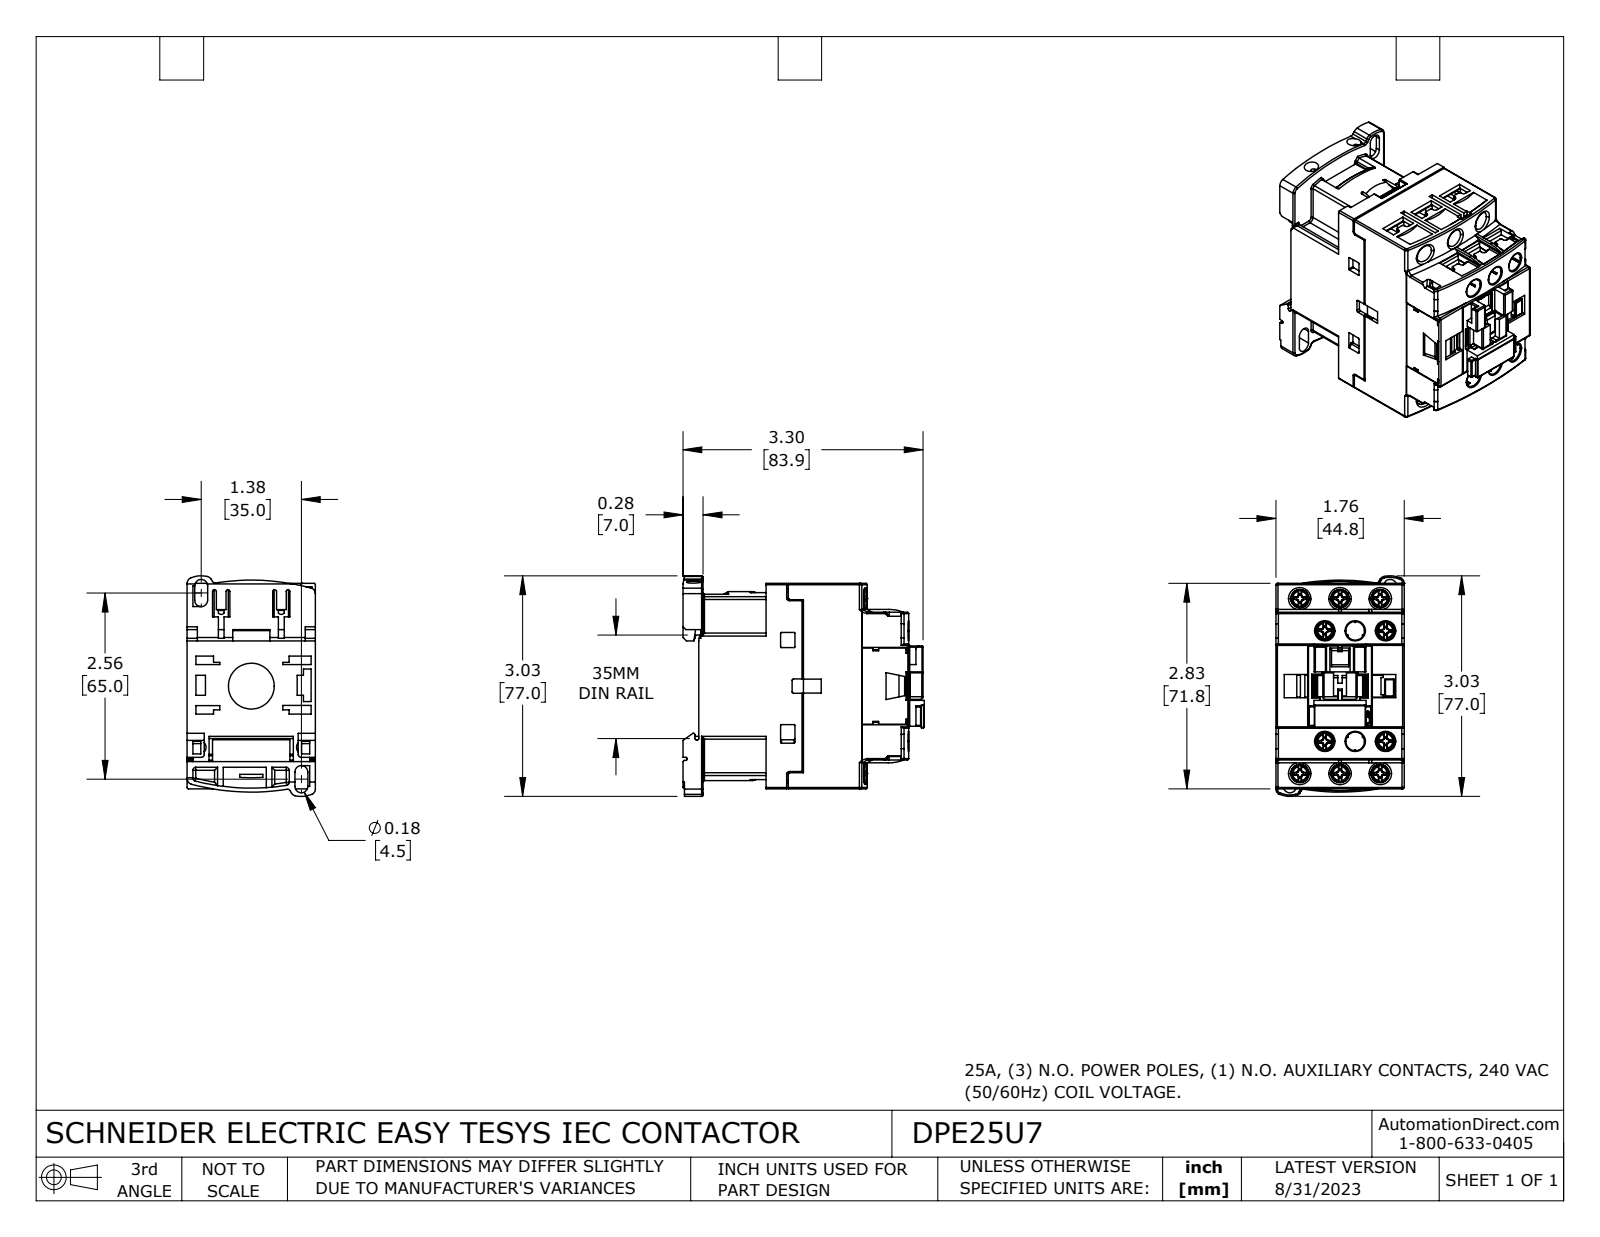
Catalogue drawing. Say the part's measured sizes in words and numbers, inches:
The part is named "DPE25U7". Its 3-D file was written by "SolidWorks 2021 (CONFIG_CONTROL_DESIGN)". It is 20 solids with 3363 faces: 2297 planar, 694 cylindrical and 372 other. Overall it measures 3.317 by 3.031 by 1.783 inches. Its volume is 8.907 cubic inches and its surface area 103.4 square inches. Round holes: 6 of diameter 0.252, 6 of diameter 0.256, 2 of diameter 0.197, 1 of diameter 0.167, 1 of diameter 0.63. Round bosses or shafts: 10 of diameter 0.138, 10 of diameter 0.108, 6 of diameter 0.315. Partial cylindrical surfaces (rounded edges, fillets, slot ends): 78 of radius 0.02, 64 of radius 0.012, 61 of radius 0.039, 42 of radius 0.006, 24 of radius 0.016, 9 of radius 0.63, 8 of radius 0.024, 7 of radius 0.079. The main face-to-face distances are 0.047, 1.764, 1.717, 0.321, 1.128, 0.807, 0.35, 2.78, 1.366, 1.118. The hole center spacings are 0.417, 0.488, 0.551, 0.558, 0.788, 0.878, 1.321, 1.576.
